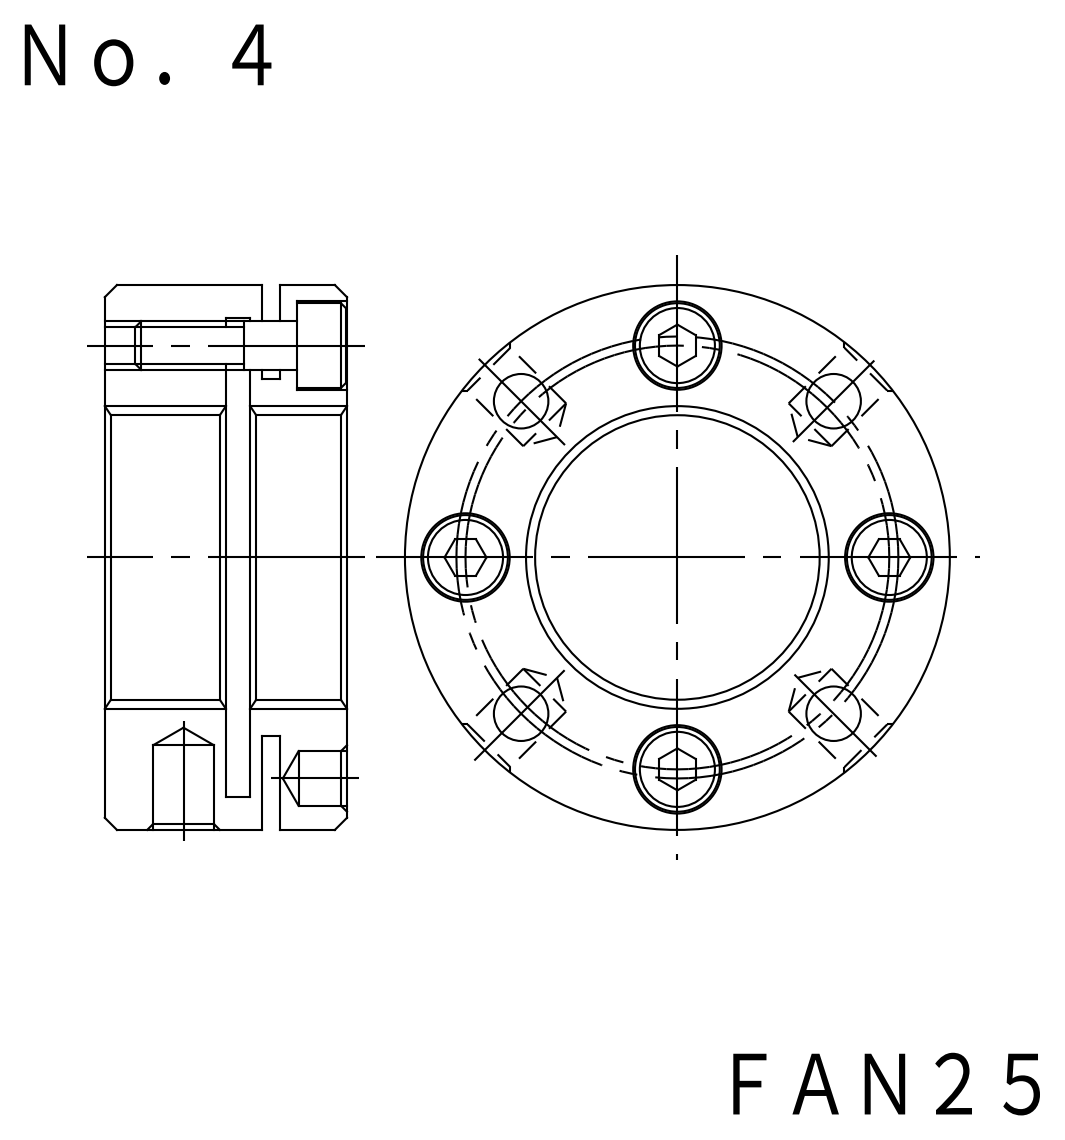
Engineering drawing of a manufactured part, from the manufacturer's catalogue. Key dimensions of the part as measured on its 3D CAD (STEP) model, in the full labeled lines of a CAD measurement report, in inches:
Part name (STEP PRODUCT): FKD FAN25; M4X14_default
STEP written by: SolidWorks 2012 (CONFIG_CONTROL_DESIGN)
Units: inches
Bodies: 5 solids, 142 faces (50 planar, 76 cylindrical, 16 other)
Overall size (bounding box): 1.772 × 1.772 × 0.787
Volume: 1.1 in³ · Surface area: 19.43 in²
Round holes (diameter × count): ⌀0.128 ×4, ⌀0.169 ×4, ⌀0.177 ×4, ⌀0.287 ×4, ⌀0.197 ×2, ⌀0.984 ×1, ⌀1.575 ×1
Round bosses / shafts (diameter × count): ⌀0.276 ×4, ⌀0.157 ×4, ⌀1.772 ×1, ⌀1.181 ×1
Main face-to-face distances: 0.079, 0.118, 0.787, 0.484, 0.303, 0.563, 0.224, 0.366, 0.197, 0.421
Hole centre spacings: 0.539, 1.3, 0.689, 0.718, 0.974, 1.016, 1.378, 1.437
